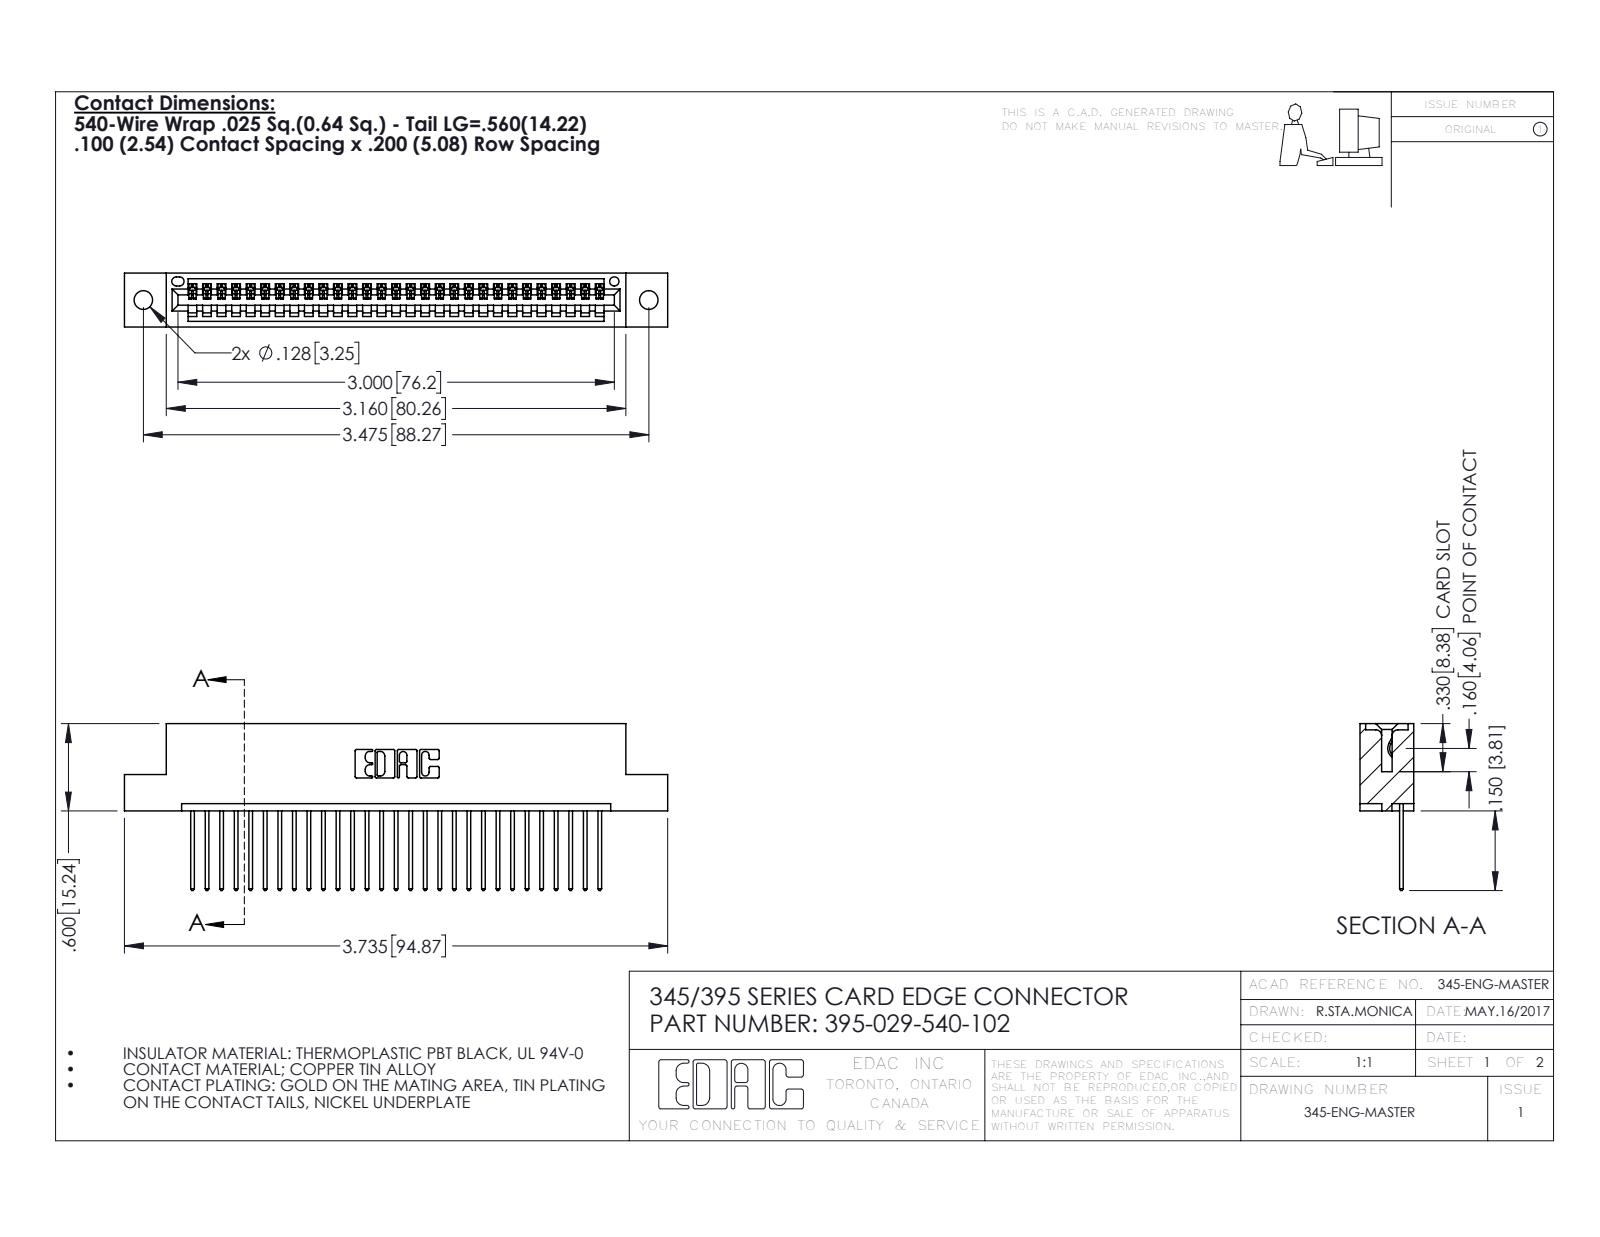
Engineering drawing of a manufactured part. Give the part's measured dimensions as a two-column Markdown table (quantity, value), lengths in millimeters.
| quantity | value |
| --- | --- |
| part name | 395-029-540-102; 345-292-001_345-293-140; 345 Part_Flush Mounting Lugs - 0.128 Dia |
| STEP written by | SolidWorks 2016 (CONFIG_CONTROL_DESIGN) |
| units | millimeters |
| bodies | 30 solids, 1808 faces (1240 planar, 568 cylindrical, 0 other) |
| overall size | 94.9 × 29.1 × 9.4 |
| volume | 8 910 mm³ |
| surface area | 11 670 mm² |
| round holes (diameter × count) | 3.3 × 2, 1.6 × 1 |
| partial cylindrical surfaces (radius × count) | 0.2 × 58, 0.3 × 58, 0.3 × 22, 0.2 × 6, 0.8 × 6, 0.7 × 3, 0.8 × 2, 1 × 2 |
| main face-to-face distances | 7.6, 1.8, 5.1, 9.4, 2.5, 6.9, 0.6, 5.7, 3.8, 1.8 |
| hole center spacings | 6.9, 82.3, 88.3 |
